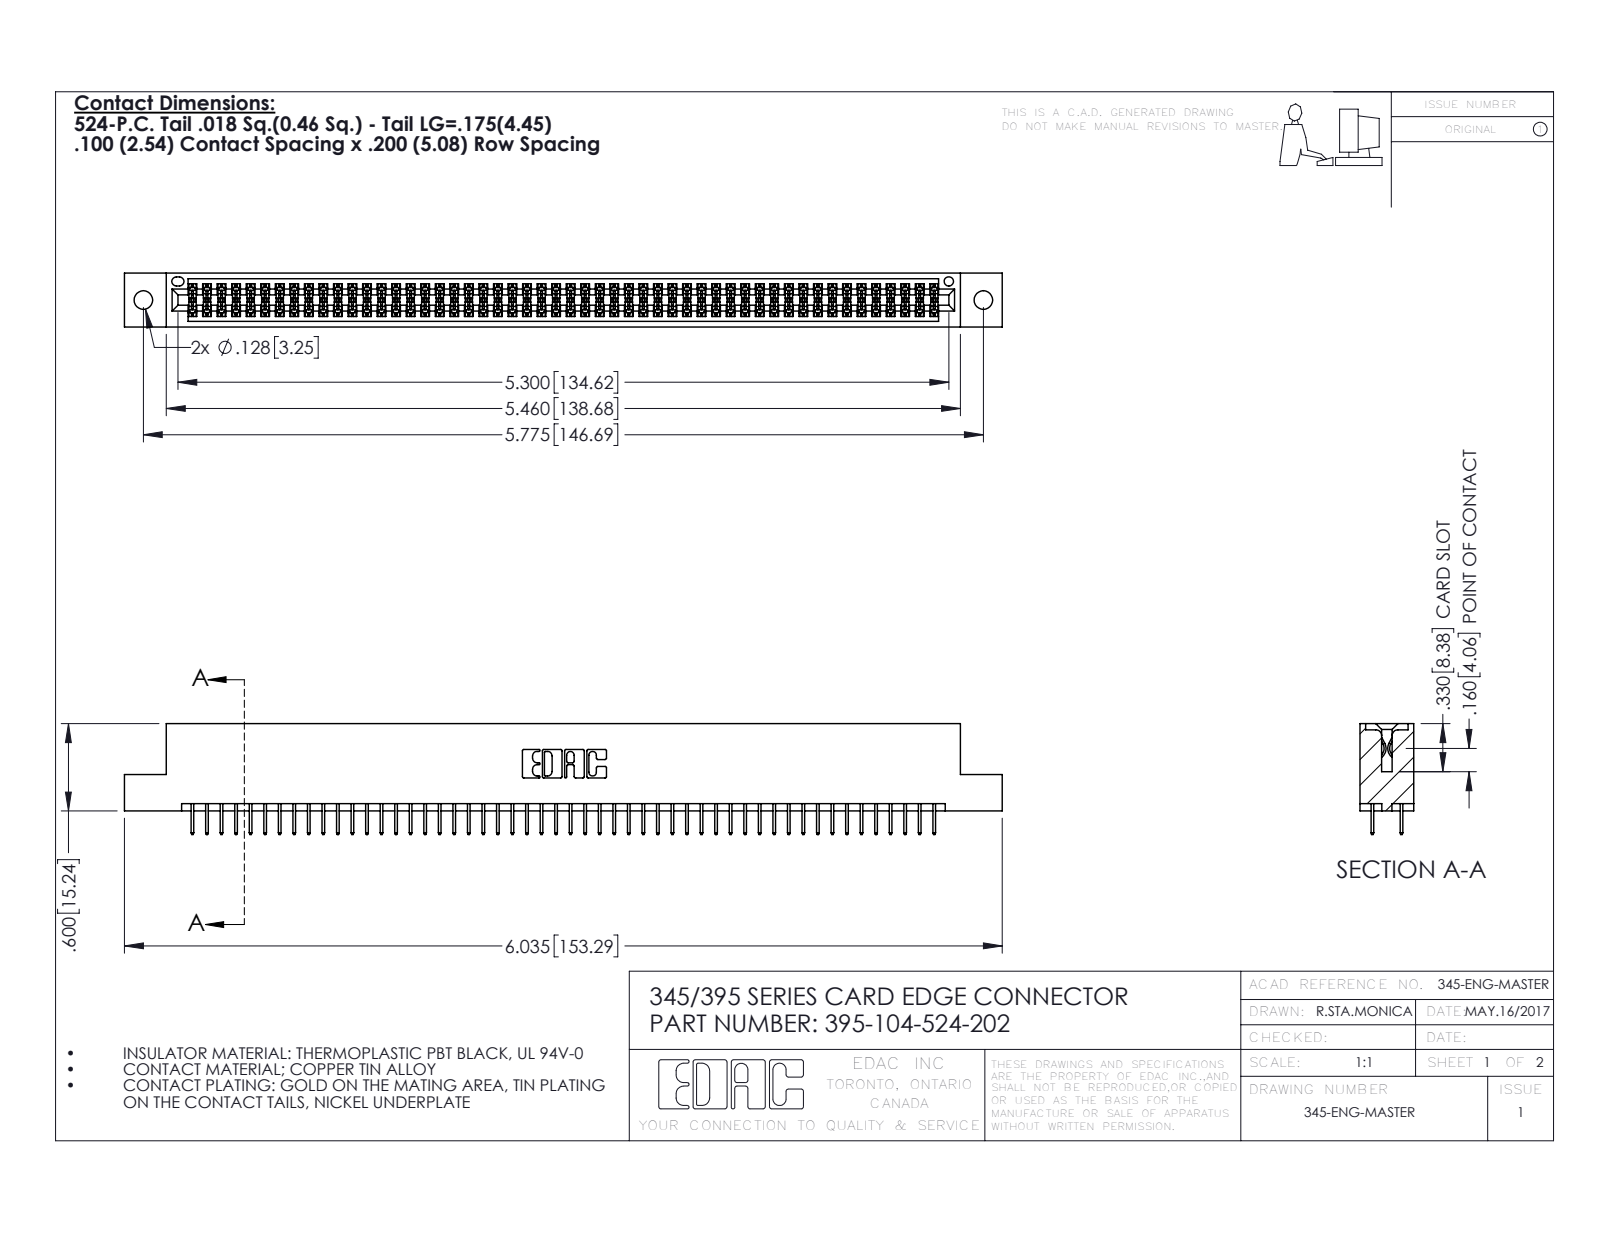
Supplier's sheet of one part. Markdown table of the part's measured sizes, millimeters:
| quantity | value |
| --- | --- |
| part name | 345-292-001_345-293-124; 345 Part_Flush Mounting Lugs - 0.128 Dia; 395-104-524-202 |
| STEP written by | SolidWorks 2016 (CONFIG_CONTROL_DESIGN) |
| units | millimeters |
| bodies | 105 solids, 5742 faces (4136 planar, 1606 cylindrical, 0 other) |
| overall size | 153.3 × 19.4 × 9.4 |
| volume | 14 800 mm³ |
| surface area | 21 370 mm² |
| round holes (diameter × count) | 3.3 × 2, 1.6 × 1 |
| partial cylindrical surfaces (radius × count) | 0.2 × 156, 0.3 × 22, 0.2 × 6, 0.8 × 6, 0.7 × 3, 0.4 × 2, 0.5 × 2, 0.6 × 2 |
| main face-to-face distances | 7.6, 1.8, 5.1, 9.4, 2.5, 6.9, 0.6, 5.7, 1.8, 4.4 |
| hole center spacings | 6.9, 140.7, 146.7 |
